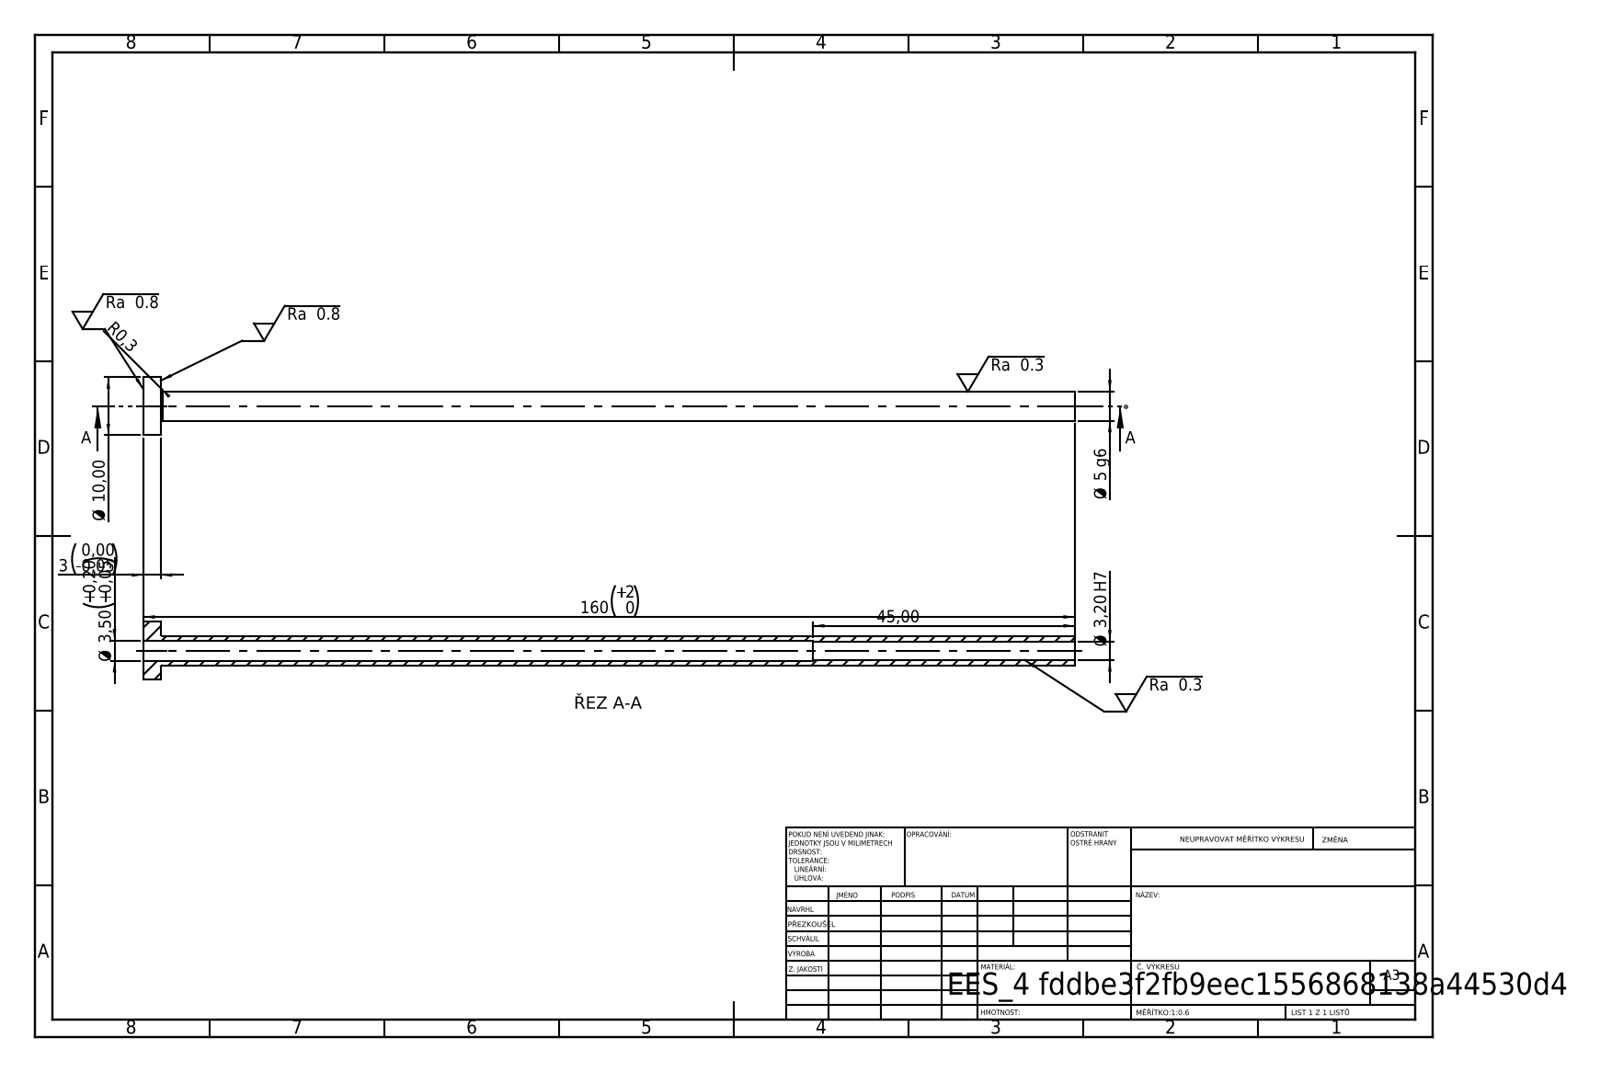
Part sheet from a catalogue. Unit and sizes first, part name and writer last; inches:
Units: inches
Overall size (bounding box): 6.299 × 0.394 × 0.394
Round holes (diameter × count): ⌀0.126 ×1, ⌀0.138 ×1
Round bosses / shafts (diameter × count): ⌀0.394 ×1, ⌀0.197 ×1
Main face-to-face distances: 0.118, 6.299, 6.181, 4.528, 4.409, 1.772
Volume: 0.113 in³ · Surface area: 6.845 in²
Bodies: 1 solid, 14 faces (4 planar, 8 cylindrical, 2 other)
STEP written by: SolidWorks 2019 (CONFIG_CONTROL_DESIGN)
